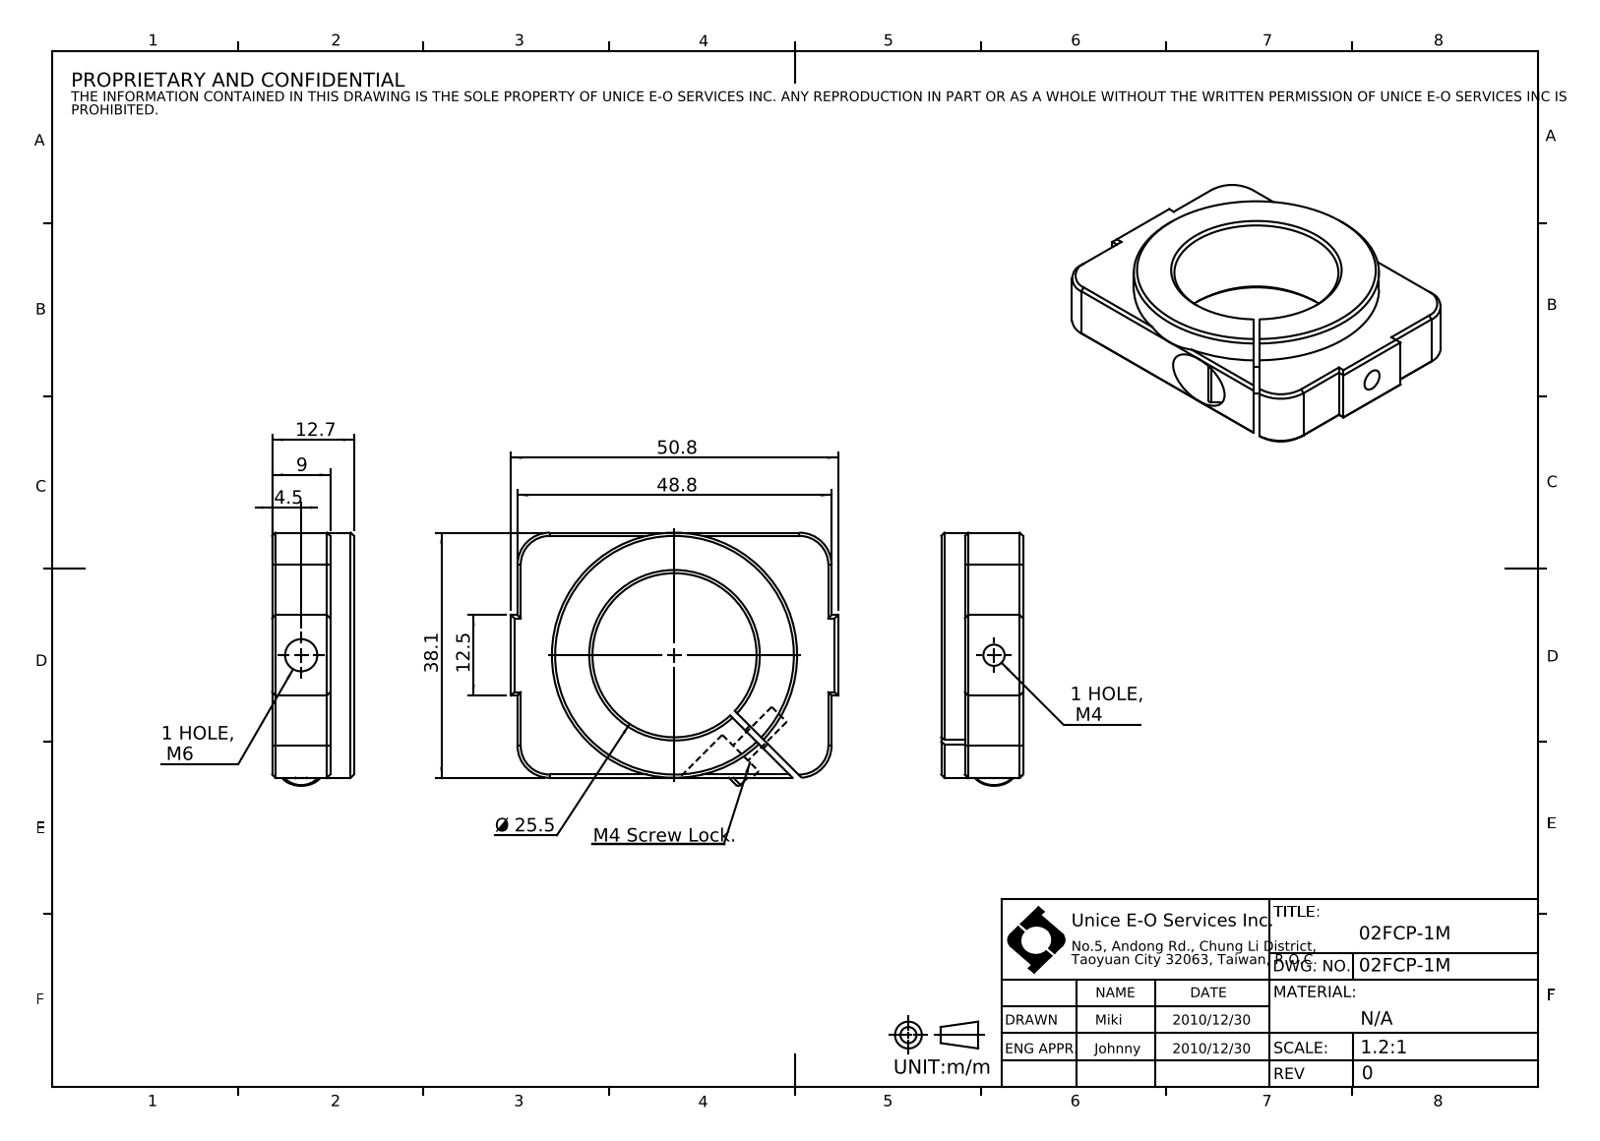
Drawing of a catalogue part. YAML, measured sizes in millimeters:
part_name: "02FCP-1M"
step_written_by: "SolidWorks 2016 (CONFIG_CONTROL_DESIGN)"
units: millimeters
bodies: {solids: 0, faces: 93, planar: 53, cylindrical: 20, other: 20}
overall_size: [50.8, 39.35, 12.7]
round_holes:
  - {diameter: 3.3, count: 1}
  - {diameter: 5, count: 1}
  - {diameter: 8, count: 1}
  - {diameter: 25.5, count: 1}
round_bosses_or_shafts:
  - {diameter: 38.1, count: 1}
  - {diameter: 7, count: 1}
  - {diameter: 4, count: 1}
partial_cylinders:
  - {radius: 5, count: 4}
face_to_face_distances: [9, 12.7, 3.7, 1, 38.1, 49.8, 48.8, 50.8, 4, 32.6]
